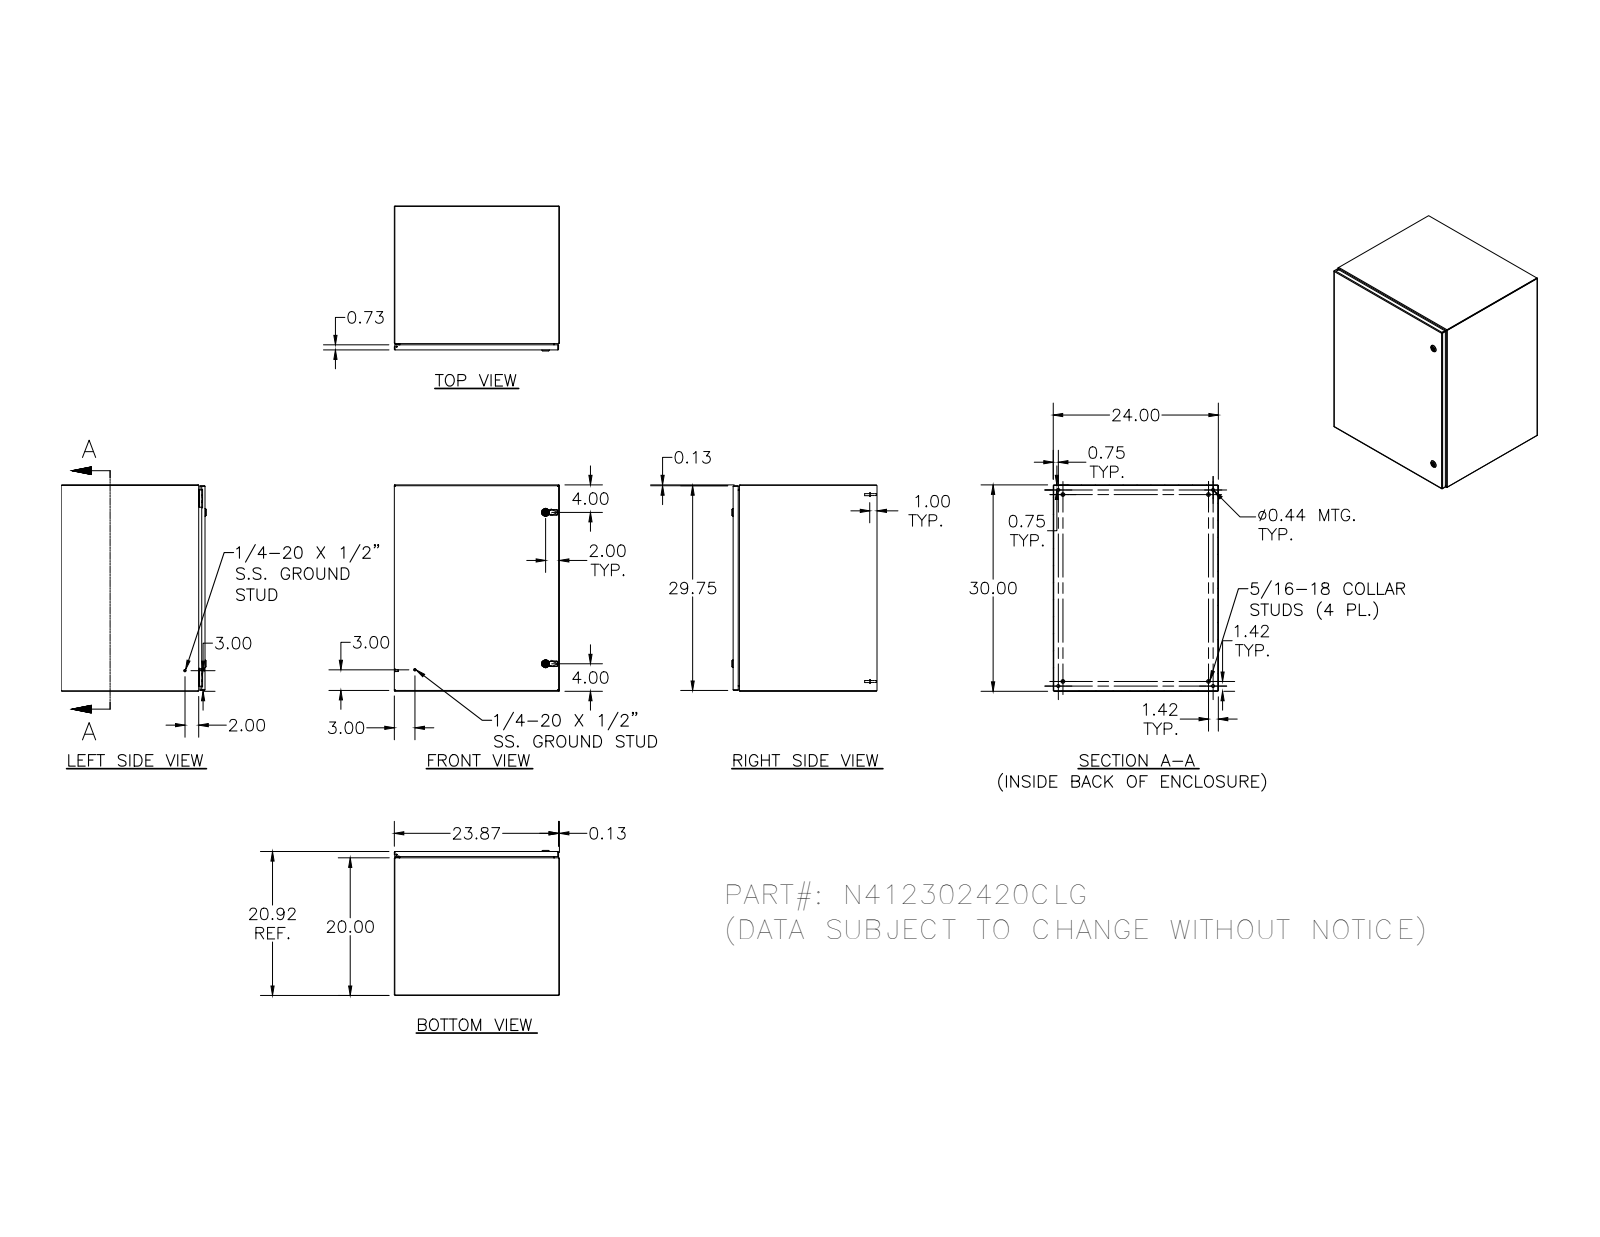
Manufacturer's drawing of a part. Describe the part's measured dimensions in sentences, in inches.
The part is named "N412302420C; N412302420CBLR; N4122420CTB; N4123024CLID (+8 more)". Its 3-D file was written by "Autodesk Inventor 2011 (AUTOMOTIVE_DESIGN)". It is 40 solids with 1822 faces: 736 planar, 662 cylindrical and 424 other. Overall it measures 30 by 24 by 21.075 inches. Its volume is 281.5 cubic inches and its surface area 7 659 square inches. Round holes: 5 of diameter 0.188, 4 of diameter 0.093, 4 of diameter 0.152, 4 of diameter 0.167, 4 of diameter 0.172, 4 of diameter 0.438, 2 of diameter 0.156, 2 of diameter 0.197, 2 of diameter 0.315, 2 of diameter 0.394, 2 of diameter 0.402, 2 of diameter 0.634. Round bosses or shafts: 10 of diameter 0.25, 4 of diameter 0.563, 4 of diameter 0.36, 4 of diameter 0.32, 4 of diameter 0.3, 4 of diameter 0.275, 4 of diameter 0.256, 4 of diameter 0.164. Partial cylindrical surfaces (rounded edges, fillets, slot ends): 54 of radius 0.012, 28 of radius 0.031, 26 of radius 0.05, 23 of radius 0.02, 18 of radius 0.016, 18 of radius 0.105, 16 of radius 0.125, 8 of radius 0.032. The main face-to-face distances are 0.074, 20.843, 23.926, 29.926, 20.769, 20.917, 23.852, 24, 29.852, 30. The hole center spacings are 26.004, 0.5, 0.656, 0.66, 0.984, 1.615, 1.618, 3.482.
